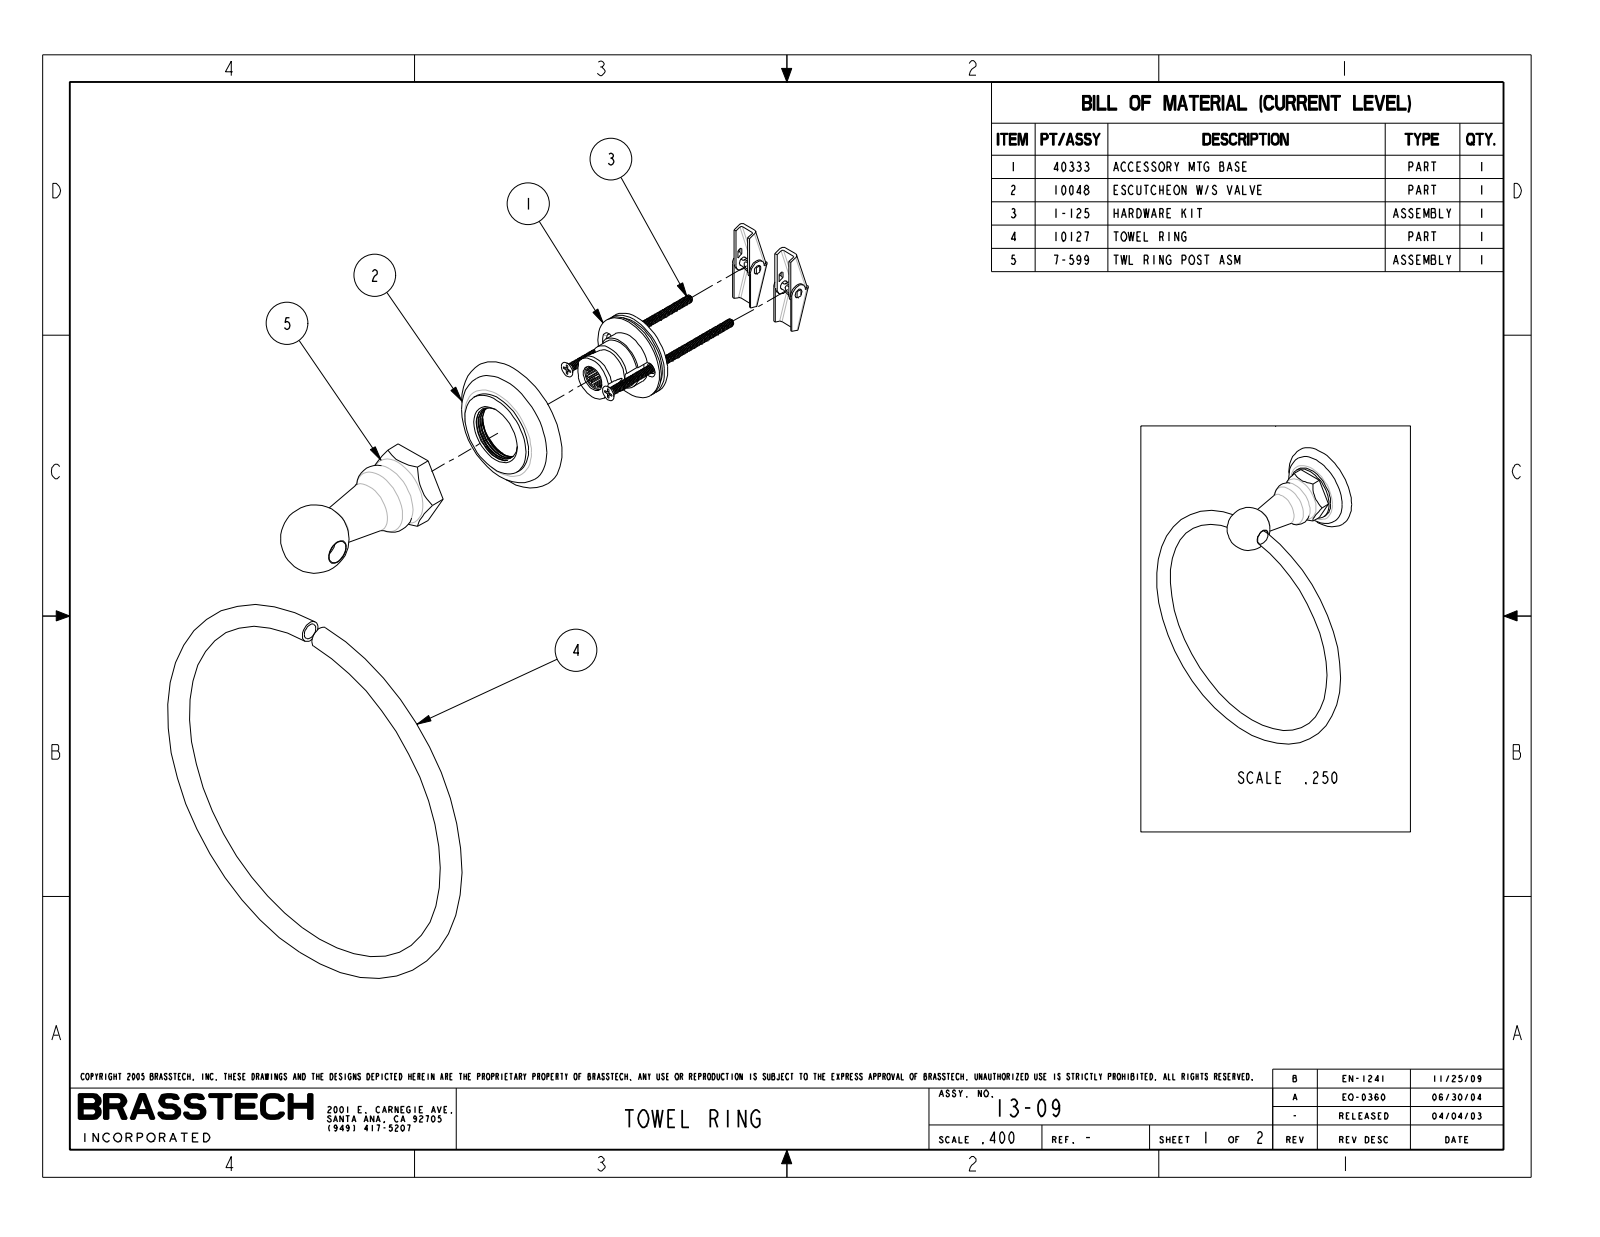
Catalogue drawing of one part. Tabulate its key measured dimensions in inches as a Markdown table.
| quantity | value |
| --- | --- |
| part name | 13-09_SW0001 |
| STEP written by | PRO/ENGINEER BY PARAMETRIC TECHNOLOGY CORPORATION, 2009300 (CONFIG_CONTROL_DESIGN) |
| units | inches |
| bodies | 0 solids, 42 faces (13 planar, 2 cylindrical, 27 other) |
| overall size | 7.993 × 7 × 3.416 |
| round bosses / shafts (diameter × count) | 1.482 × 1 |
| main face-to-face distances | 0.375, 0.437, 0.062, 1.25, 1.25, 1.098, 0.05, 1.2 |
